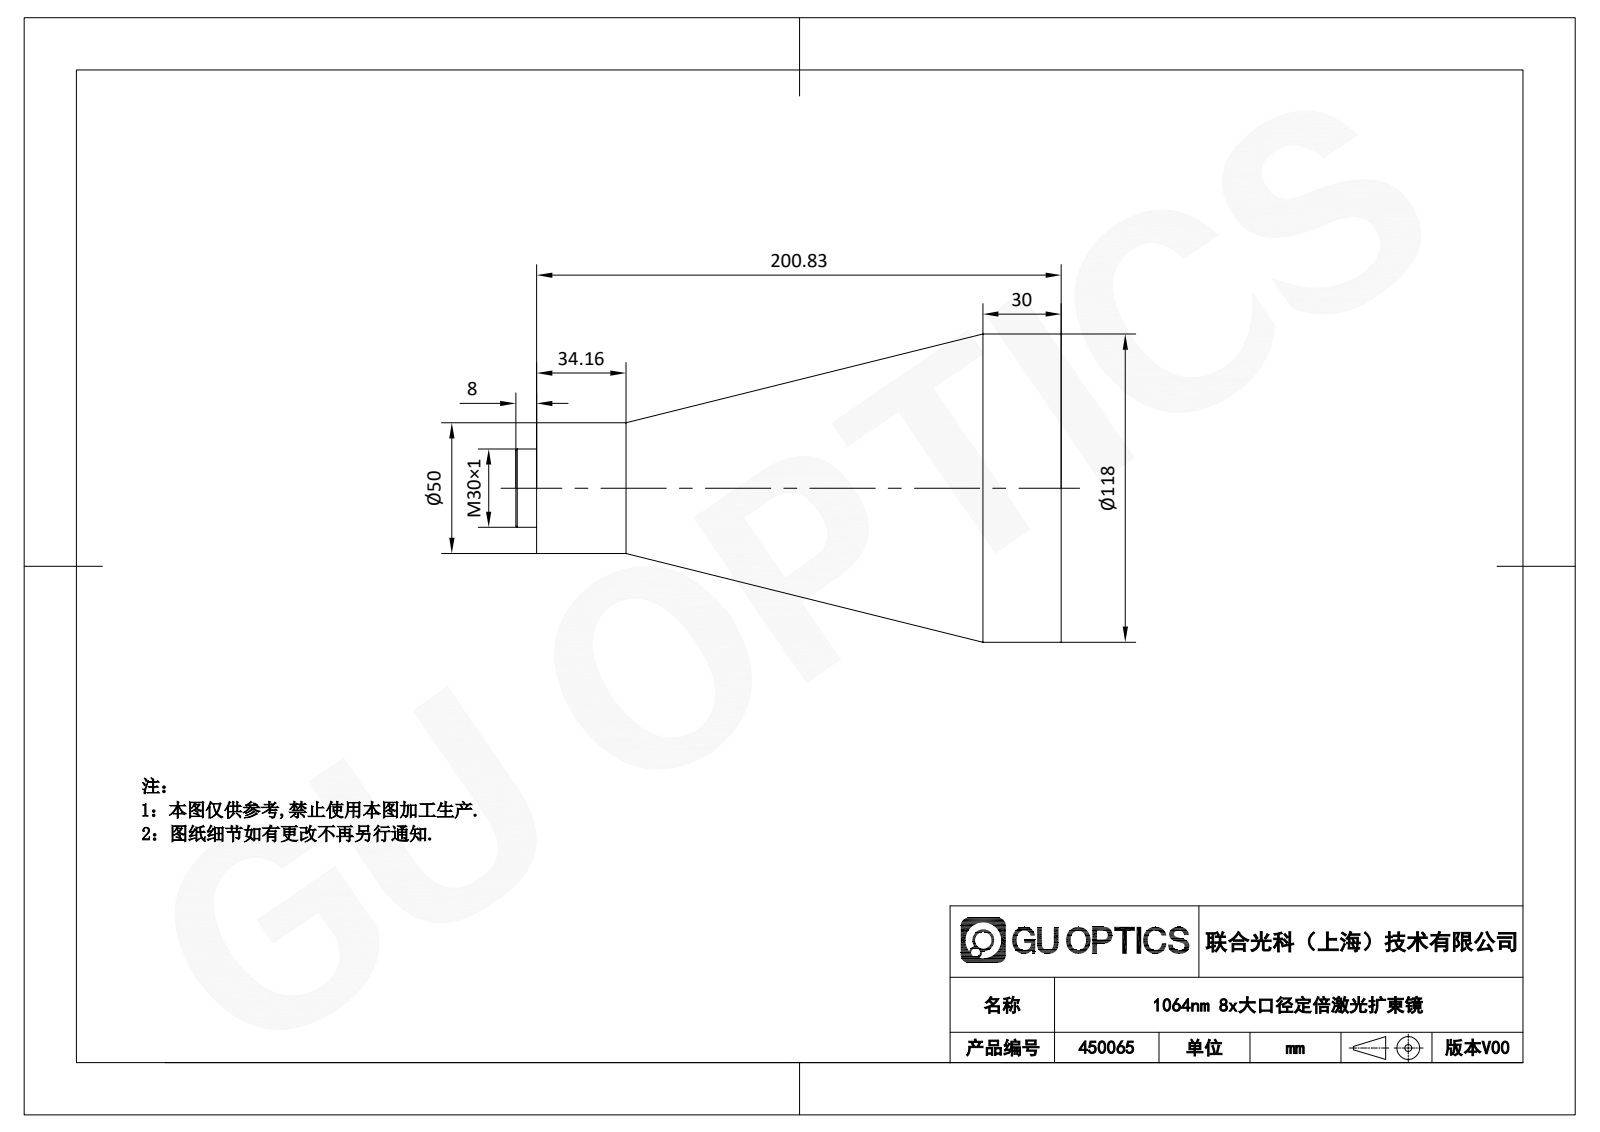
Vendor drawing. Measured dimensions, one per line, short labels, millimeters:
name: 450065
written by: SolidWorks 2020 (AUTOMOTIVE_DESIGN)
unit: mm
bodies: 1 solid, 13 faces (3 planar, 6 cylindrical, 4 other)
size: 208.83 × 118 × 118
volume: 1 200 000 mm³; area: 67 278 mm²
bosses: 1× ⌀118, 1× ⌀50, 1× ⌀30
face distances: 200.83, 208.83, 8
